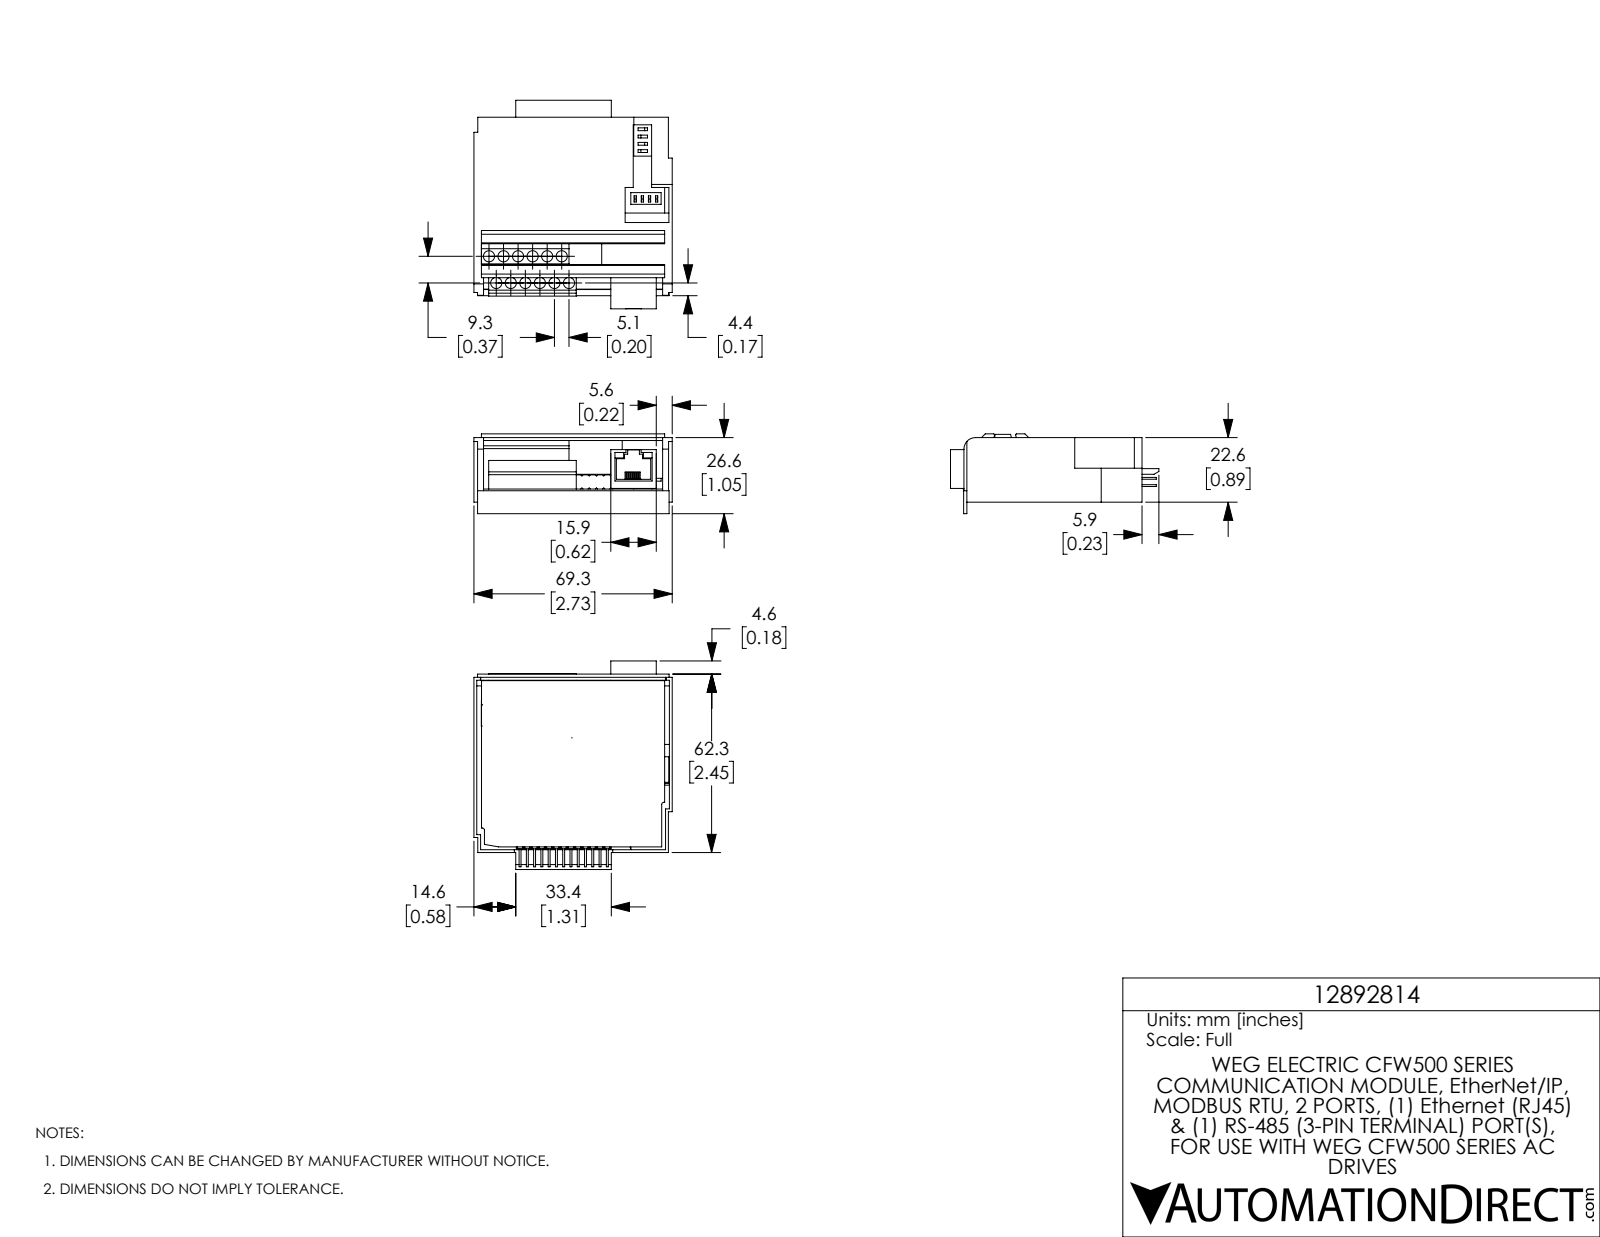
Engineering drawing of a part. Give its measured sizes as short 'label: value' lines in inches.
name: 12892814_MODULO COMUNICACAO CFW500_CETH_IP Coord nc
written by: SolidWorks 2017 (AUTOMOTIVE_DESIGN)
unit: in
bodies: 7 solids, 549 faces (519 planar, 30 cylindrical, 0 other)
size: 2.866 × 2.726 × 1.096
volume: 1.67 in³; area: 50.58 in²
holes: 12× ⌀0.154
rounds: 2× R0.03, 1× R0.118, 1× R0.157
face distances: 0.039, 0.063, 0.73, 0.667, 0.707, 0.77, 2.687, 2.727, 0.051, 2.413
hole spacings: 0.38, 0.2, 0.473, 0.4, 0.62, 0.6, 0.79, 0.8
